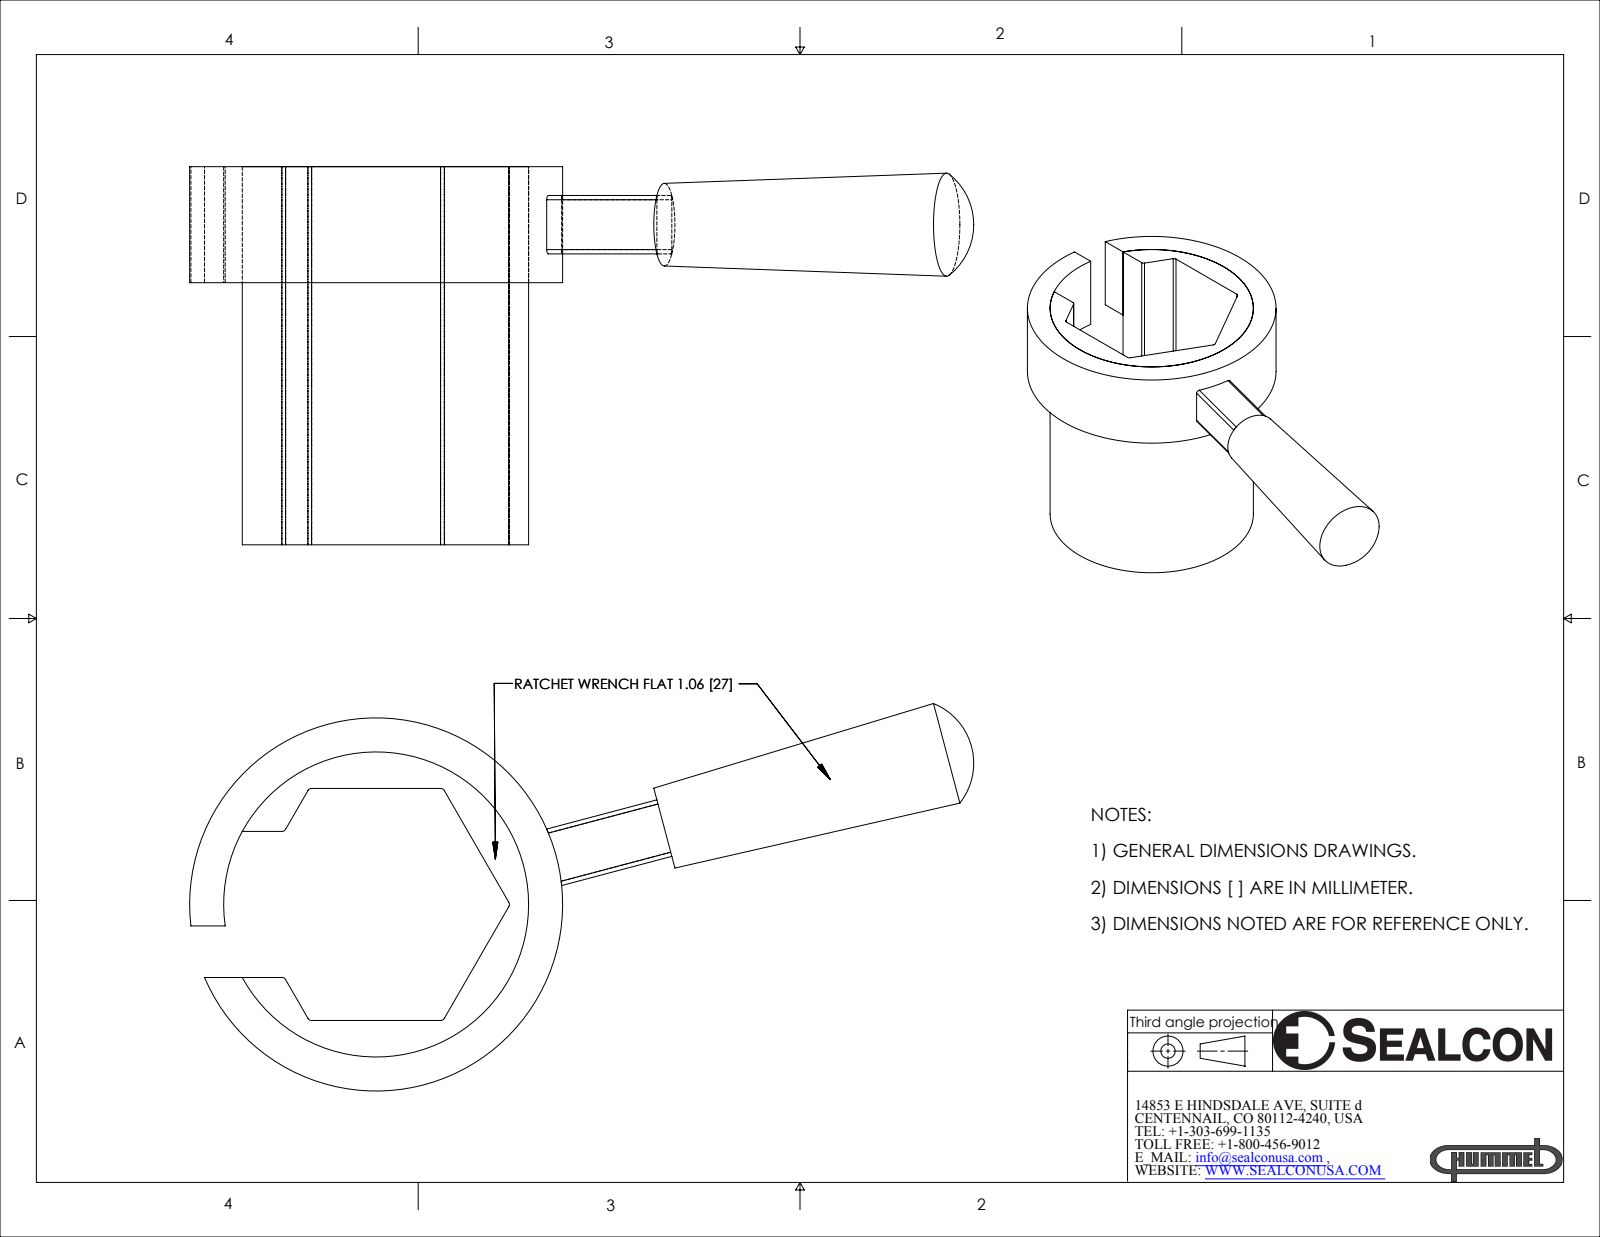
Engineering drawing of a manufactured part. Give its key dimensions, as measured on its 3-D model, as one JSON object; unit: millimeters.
{"part_name": "R-2700-WR", "step_written_by": "SolidWorks 2007 (CONFIG_CONTROL_DESIGN)", "units": "millimeters", "bodies": {"solids": 3, "faces": 43, "planar": 19, "cylindrical": 20, "other": 4}, "overall_size": [91.28, 45.09, 44], "volume_mm3": 23055, "surface_area_mm2": 14316, "round_holes": [[35.5, 1]], "round_bosses_or_shafts": [[43.42, 1]], "partial_cylinders_radius": [[0.5, 11]], "face_to_face_distances": [27, 13.5, 5, 22, 30.5, 44, 17, 6.8, 3.35, 10.15]}
